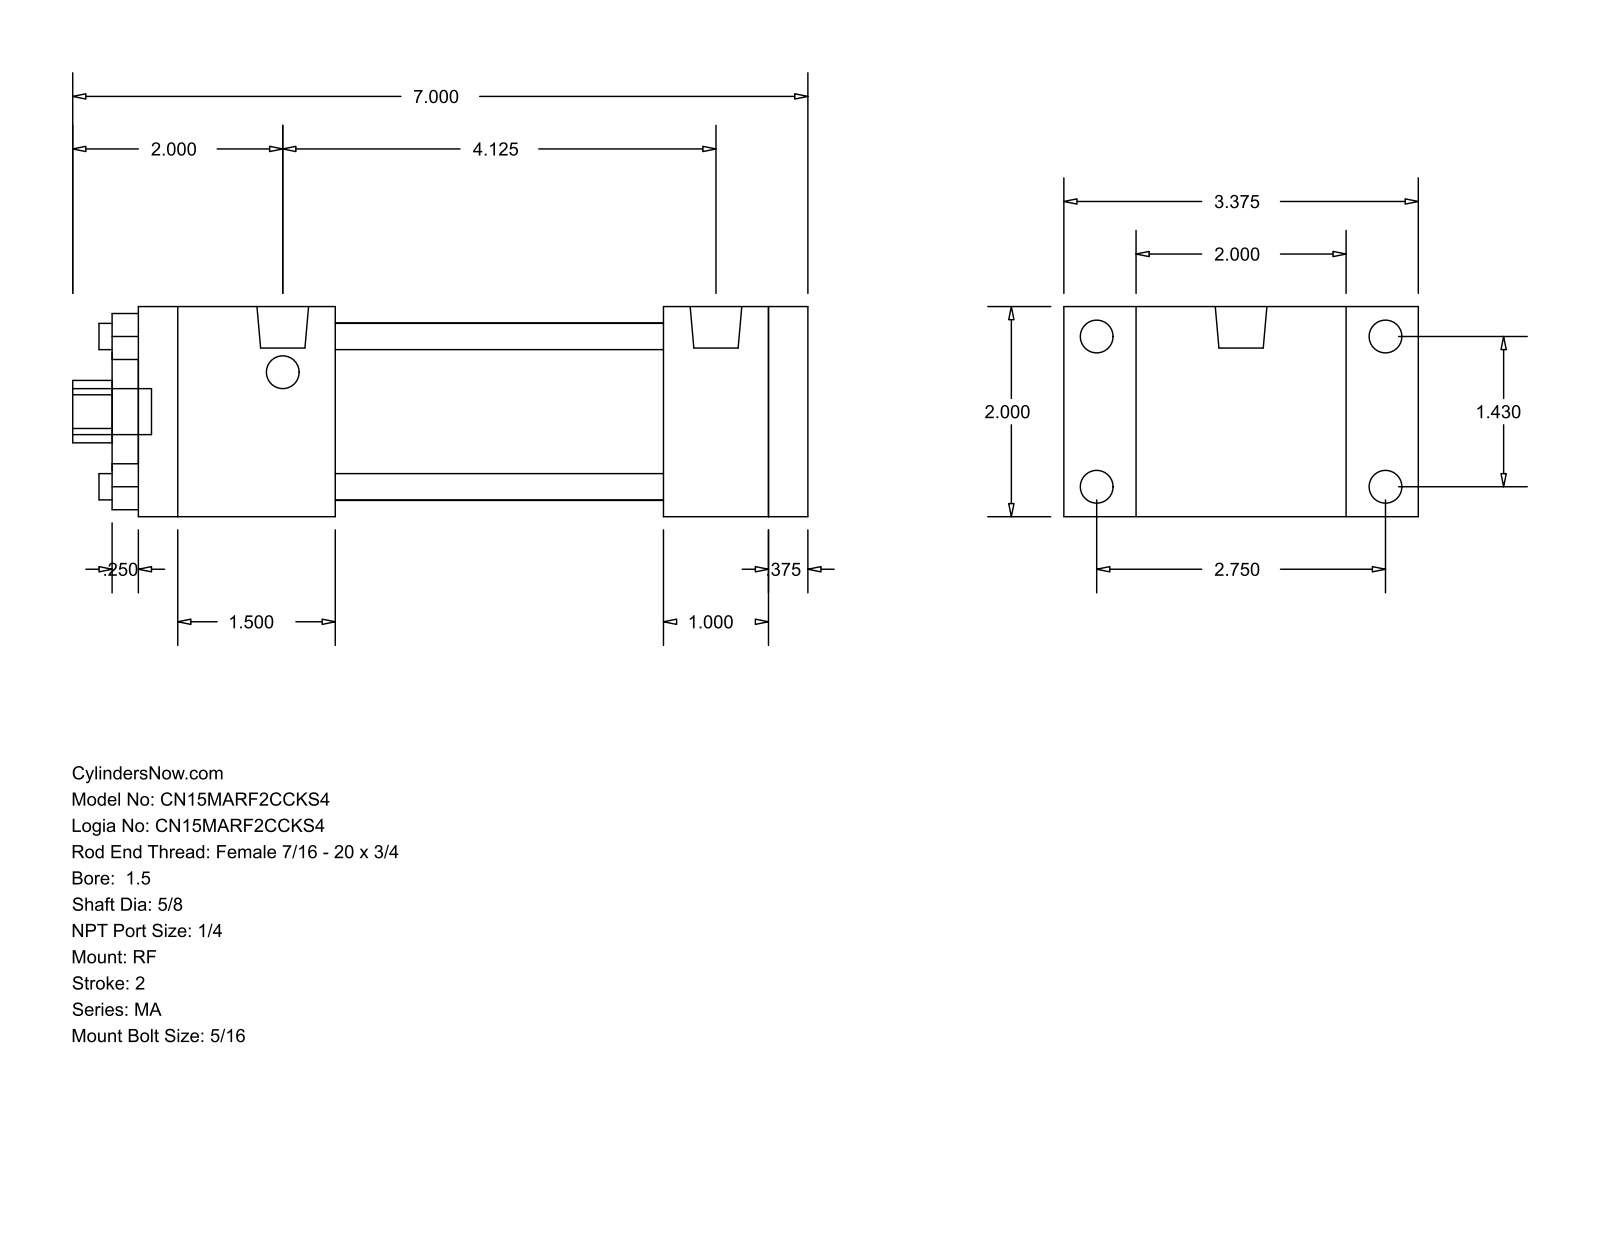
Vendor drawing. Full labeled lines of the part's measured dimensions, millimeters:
Part name (STEP PRODUCT): MA_RF__0150_0.625
STEP written by: GSSL Pune (CONFIG_CONTROL_DESIGN)
Units: millimetres
Bodies: 0 solids, 92 faces (64 planar, 28 cylindrical, 0 other)
Overall size (bounding box): 177.8 × 85.72 × 50.8
Round holes (diameter × count): ⌀6.35 ×4, ⌀15.88 ×1, ⌀28.57 ×1, ⌀42.93 ×1
Round bosses / shafts (diameter × count): ⌀7.94 ×8, ⌀12.49 ×2, ⌀11.11 ×1
Partial cylindrical surfaces — rounded edges, fillets, slot ends (radius × count): R7.54 ×1
Main face-to-face distances: 50.8, 9.52, 152.4, 161.92, 127, 25.4, 34.92, 47.62, 79.38, 104.78
Hole centre spacings: 25.68, 36.32, 51.36
